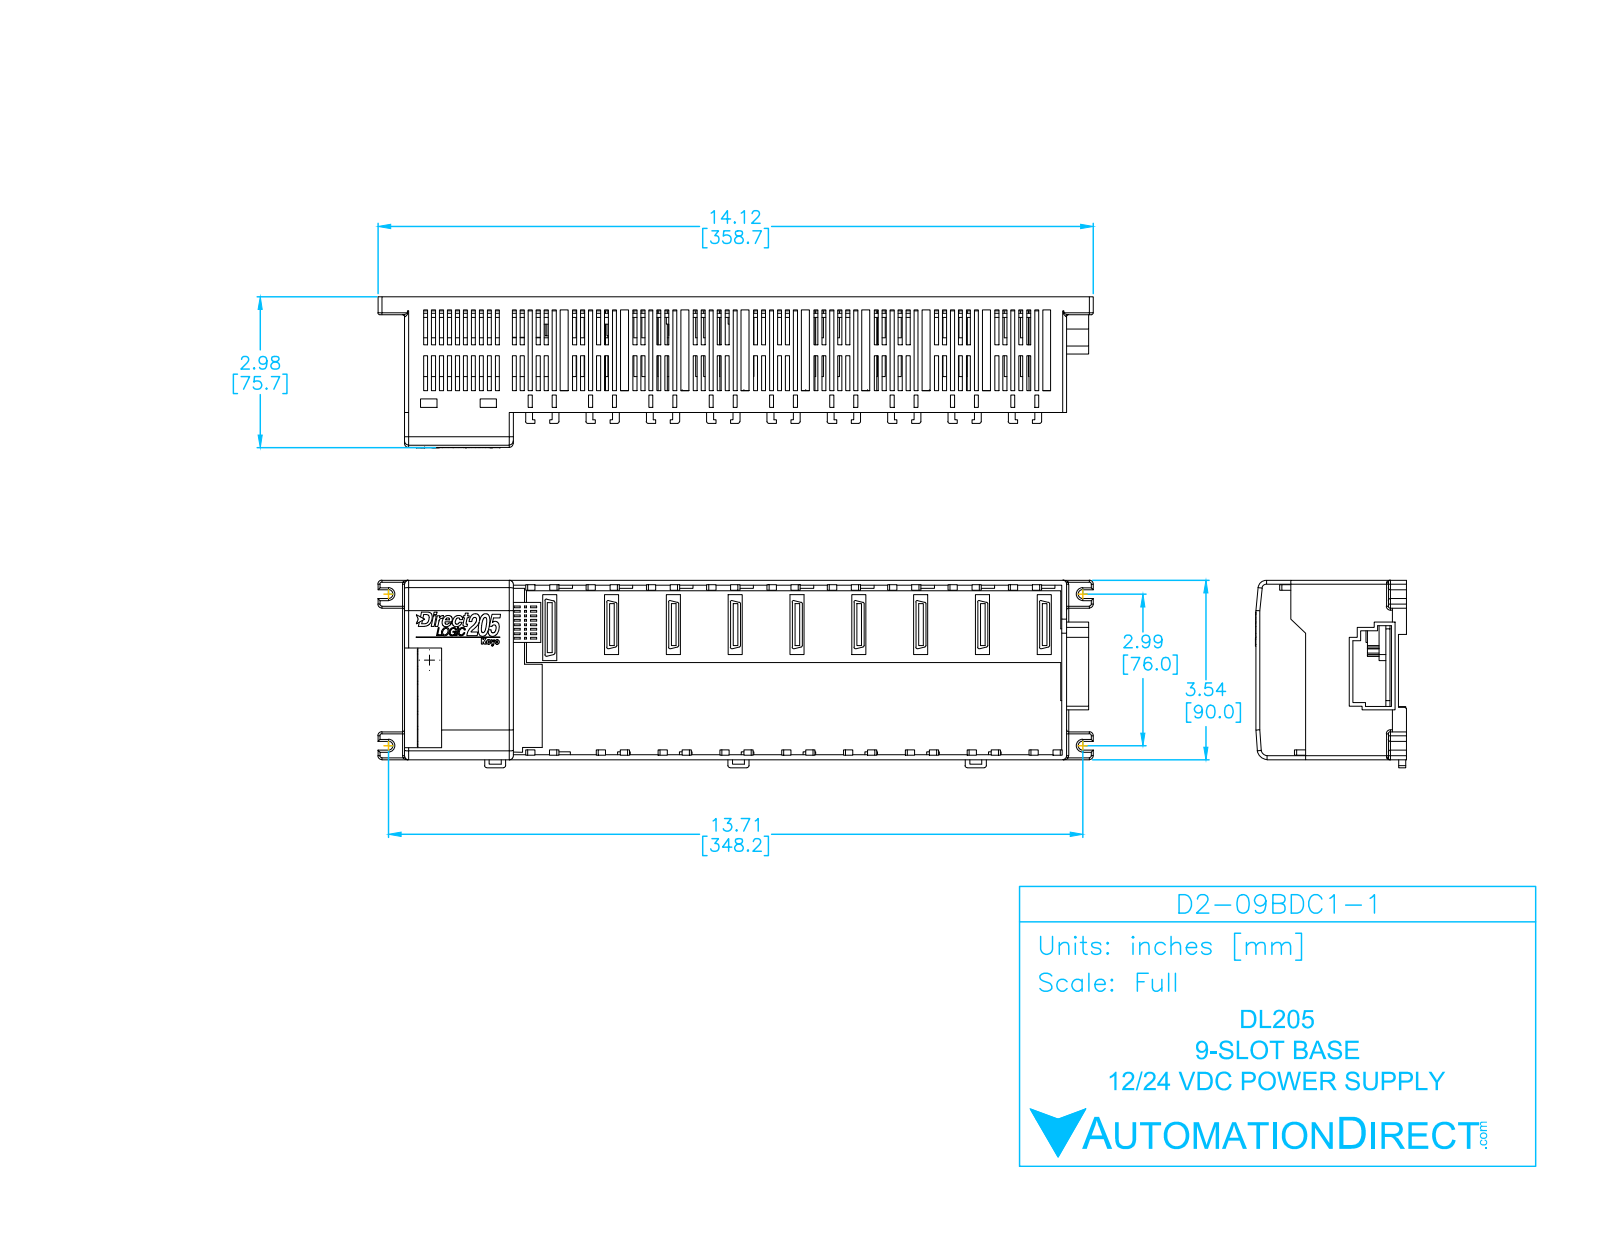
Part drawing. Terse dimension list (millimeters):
name: D2-09BDC1-1
written by: SolidWorks 2009 (AUTOMOTIVE_DESIGN)
unit: mm
bodies: 7 solids, 3025 faces (2640 planar, 219 cylindrical, 166 other)
size: 358.68 × 94 × 75.7
volume: 354 279 mm³; area: 251 686 mm²
bosses: 6× ⌀5.42
rounds: 86× R1, 36× R0.75, 24× R0.25, 20× R2, 4× R2.21, 4× R4.71, 1× R4.12, 1× R5.29
face distances: 2.5, 3, 85, 1.25, 87.5, 2, 4.25, 6.25, 3.25, 90
